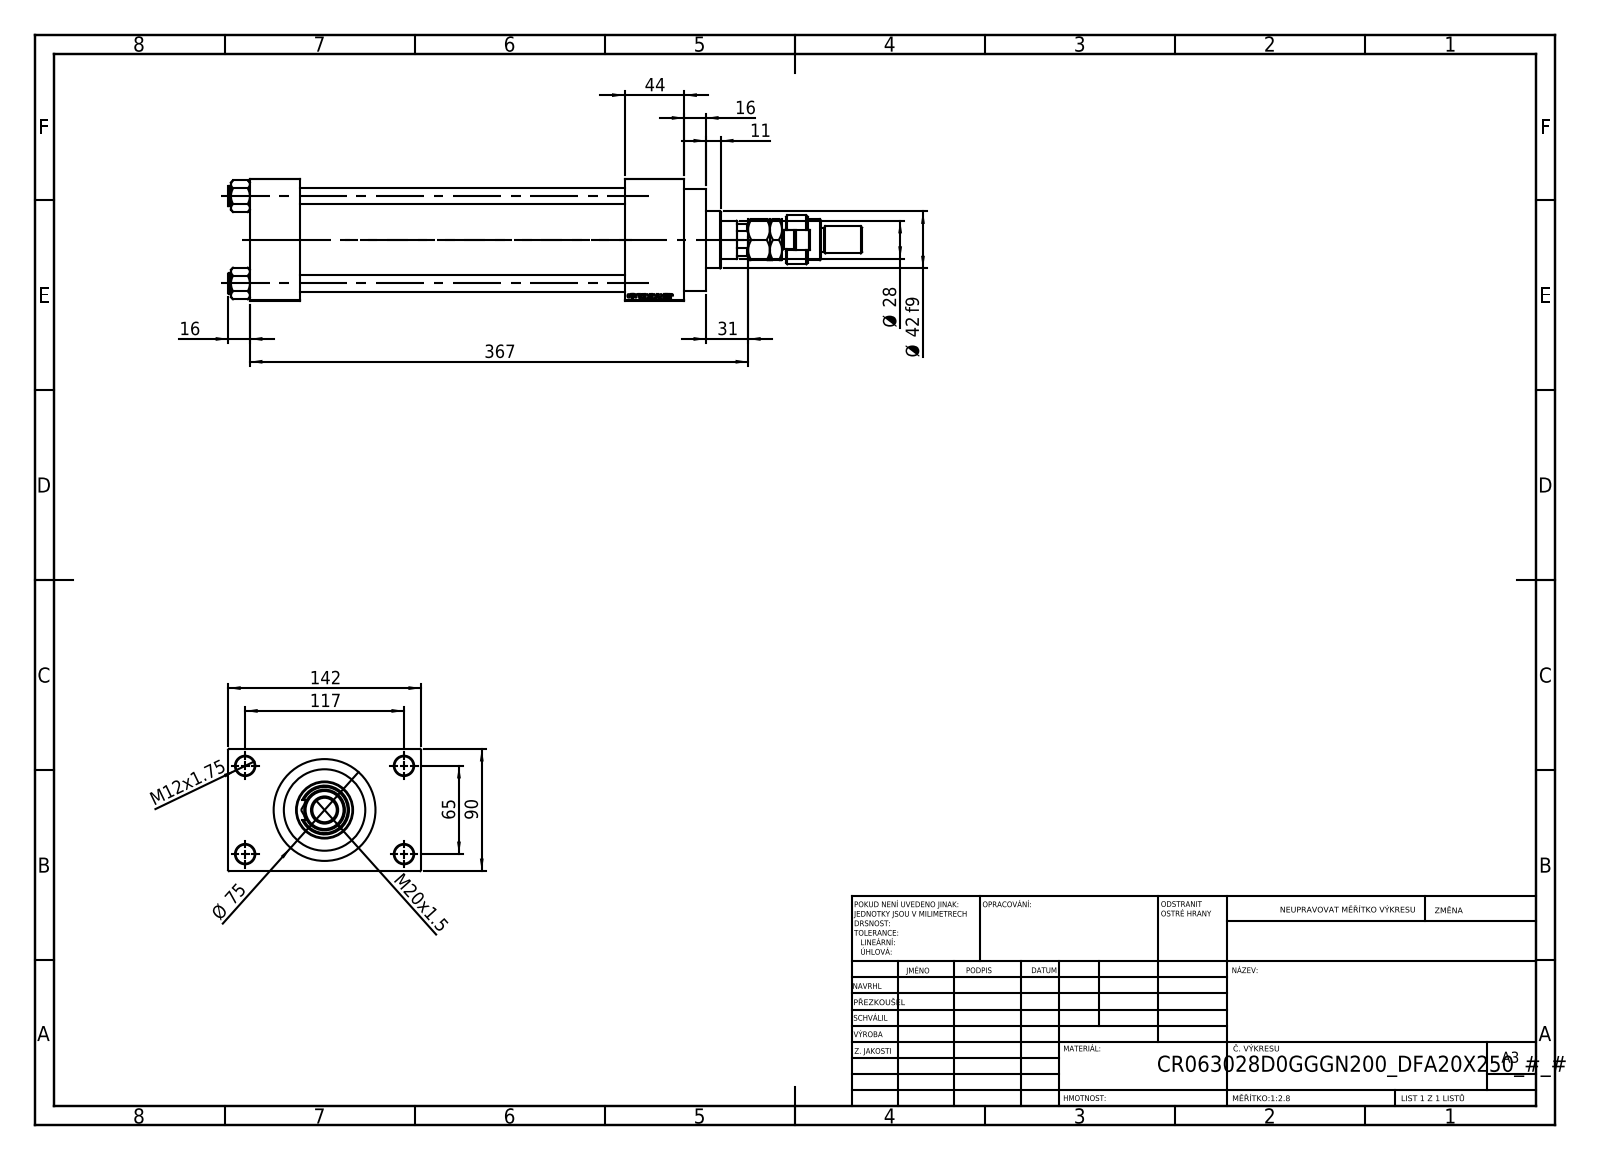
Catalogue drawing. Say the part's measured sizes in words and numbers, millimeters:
The part is named "V215CR_D_TYCINKA; V215_VC_A; V215CR_VCP_D; V215CR_D_Body (+3 more)". Its 3-D file was written by "SolidWorks 2019 (CONFIG_CONTROL_DESIGN)". It is 13 solids with 1189 faces: 525 planar, 102 cylindrical and 562 other. Overall it measures 467 by 142 by 90 millimeters. Its volume is 1 458 000 cubic millimeters and its surface area 329 471 square millimeters. Round holes: 4 of diameter 12, 4 of diameter 14, 2 of diameter 7, 2 of diameter 20.96, 2 of diameter 30, 1 of diameter 18.5, 1 of diameter 28, 1 of diameter 31, 1 of diameter 50, 1 of diameter 60, 1 of diameter 63. Round bosses or shafts: 4 of diameter 15, 1 of diameter 75, 1 of diameter 69, 1 of diameter 42, 1 of diameter 36, 1 of diameter 30, 1 of diameter 22, 1 of diameter 20. Partial cylindrical surfaces (rounded edges, fillets, slot ends): 1 of radius 7.5, 1 of radius 12, 1 of radius 13.5. The main face-to-face distances are 90, 239, 37, 276, 44, 320, 283, 116, 26, 142. The hole center spacings are 26.35, 45.47, 64.3, 66.92, 69.81, 90.65, 111.34, 65.
